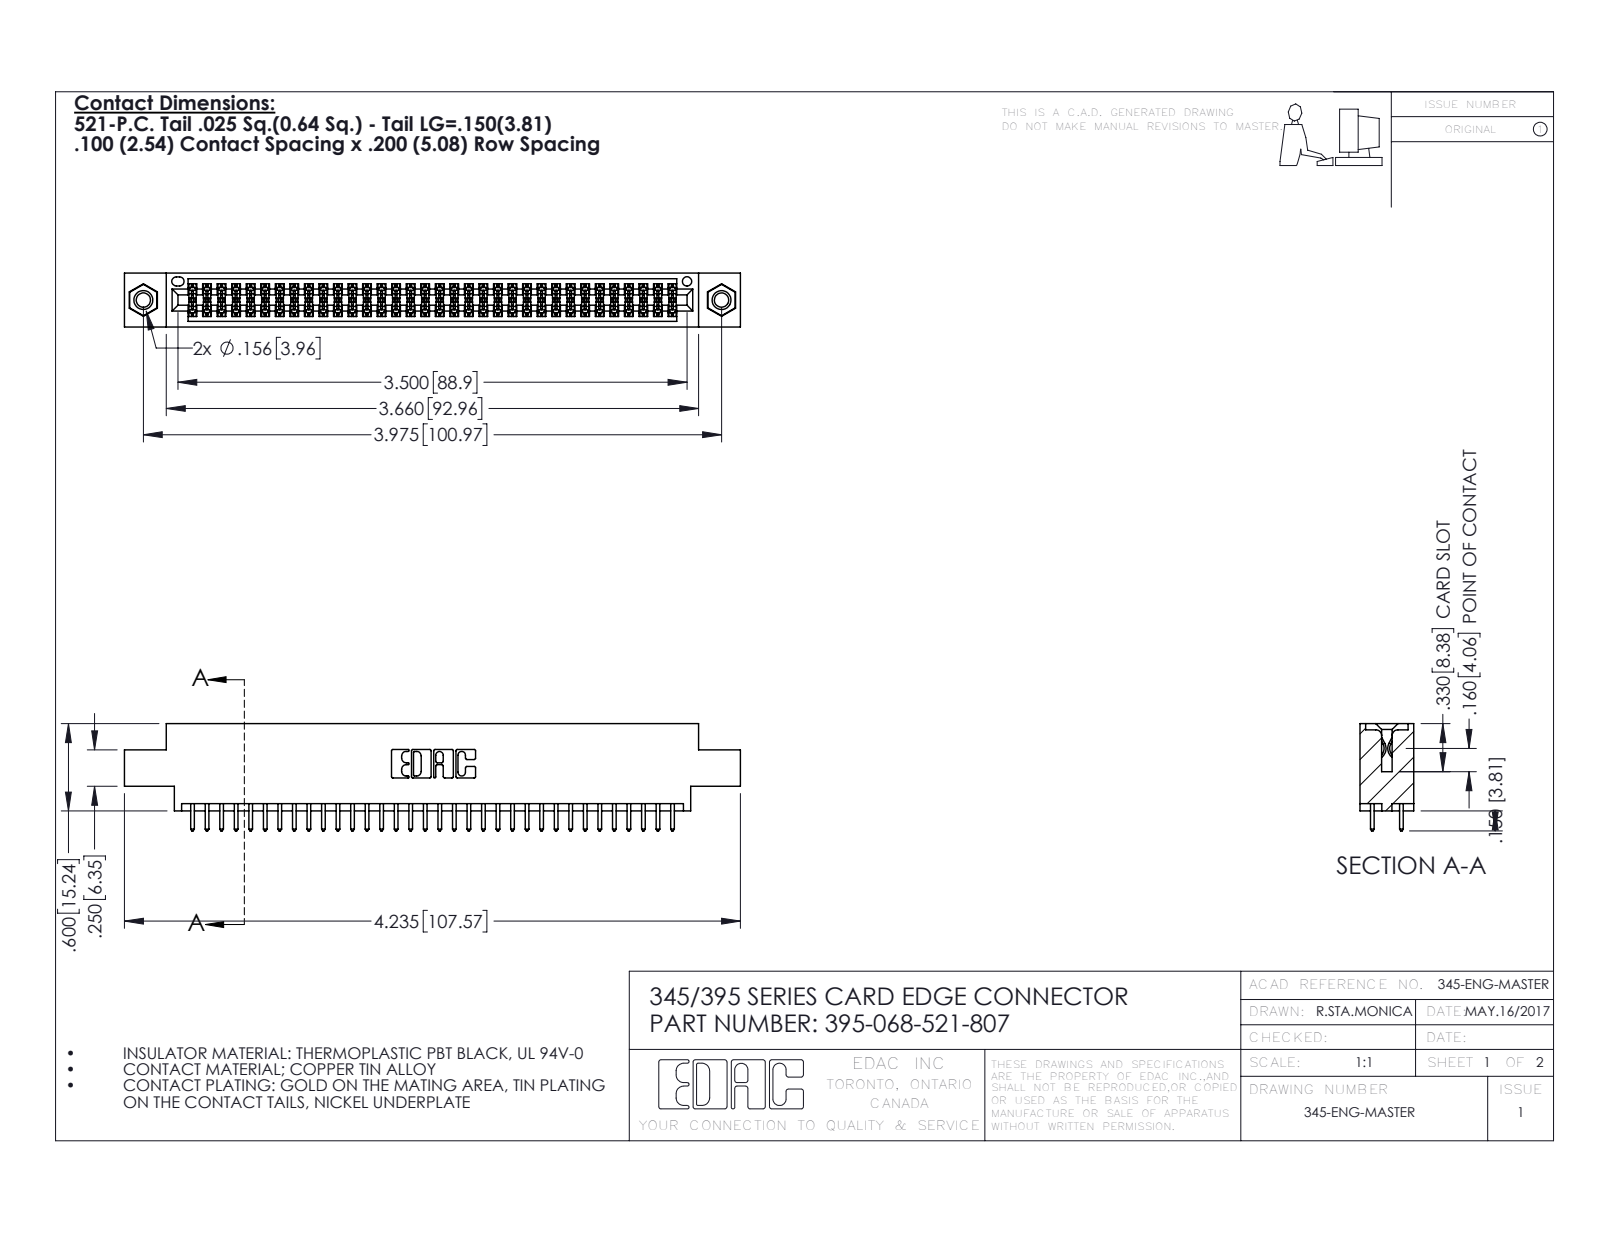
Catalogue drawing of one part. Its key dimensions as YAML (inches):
part_name: "345 Part_0.170 Offset - 0.156 Dia-TI; 345-292-001_345-293-121; 345-250-001_345-250-005-103; 395-068-521-807"
step_written_by: "SolidWorks 2016 (CONFIG_CONTROL_DESIGN)"
units: inches
bodies: {solids: 71, faces: 3590, planar: 2360, cylindrical: 1214, other: 16}
overall_size: [4.235, 0.737, 0.37]
volume: 0.624
surface_area: 23.16
round_holes:
  - {diameter: 0.098, count: 2}
  - {diameter: 0.125, count: 2}
  - {diameter: 0.156, count: 2}
  - {diameter: 0.064, count: 1}
round_bosses_or_shafts:
  - {diameter: 0.155, count: 2}
partial_cylinders:
  - {radius: 0.006, count: 102}
  - {radius: 0.01, count: 68}
  - {radius: 0.01, count: 22}
  - {radius: 0.007, count: 6}
  - {radius: 0.031, count: 6}
  - {radius: 0.026, count: 3}
  - {radius: 0.014, count: 2}
  - {radius: 0.019, count: 2}
face_to_face_distances: [0.072, 0.298, 0.2, 0.37, 0.098, 0.272, 0.025, 0.225, 0.175, 0.149]
hole_center_spacings: [0.27, 3.74, 3.975]
